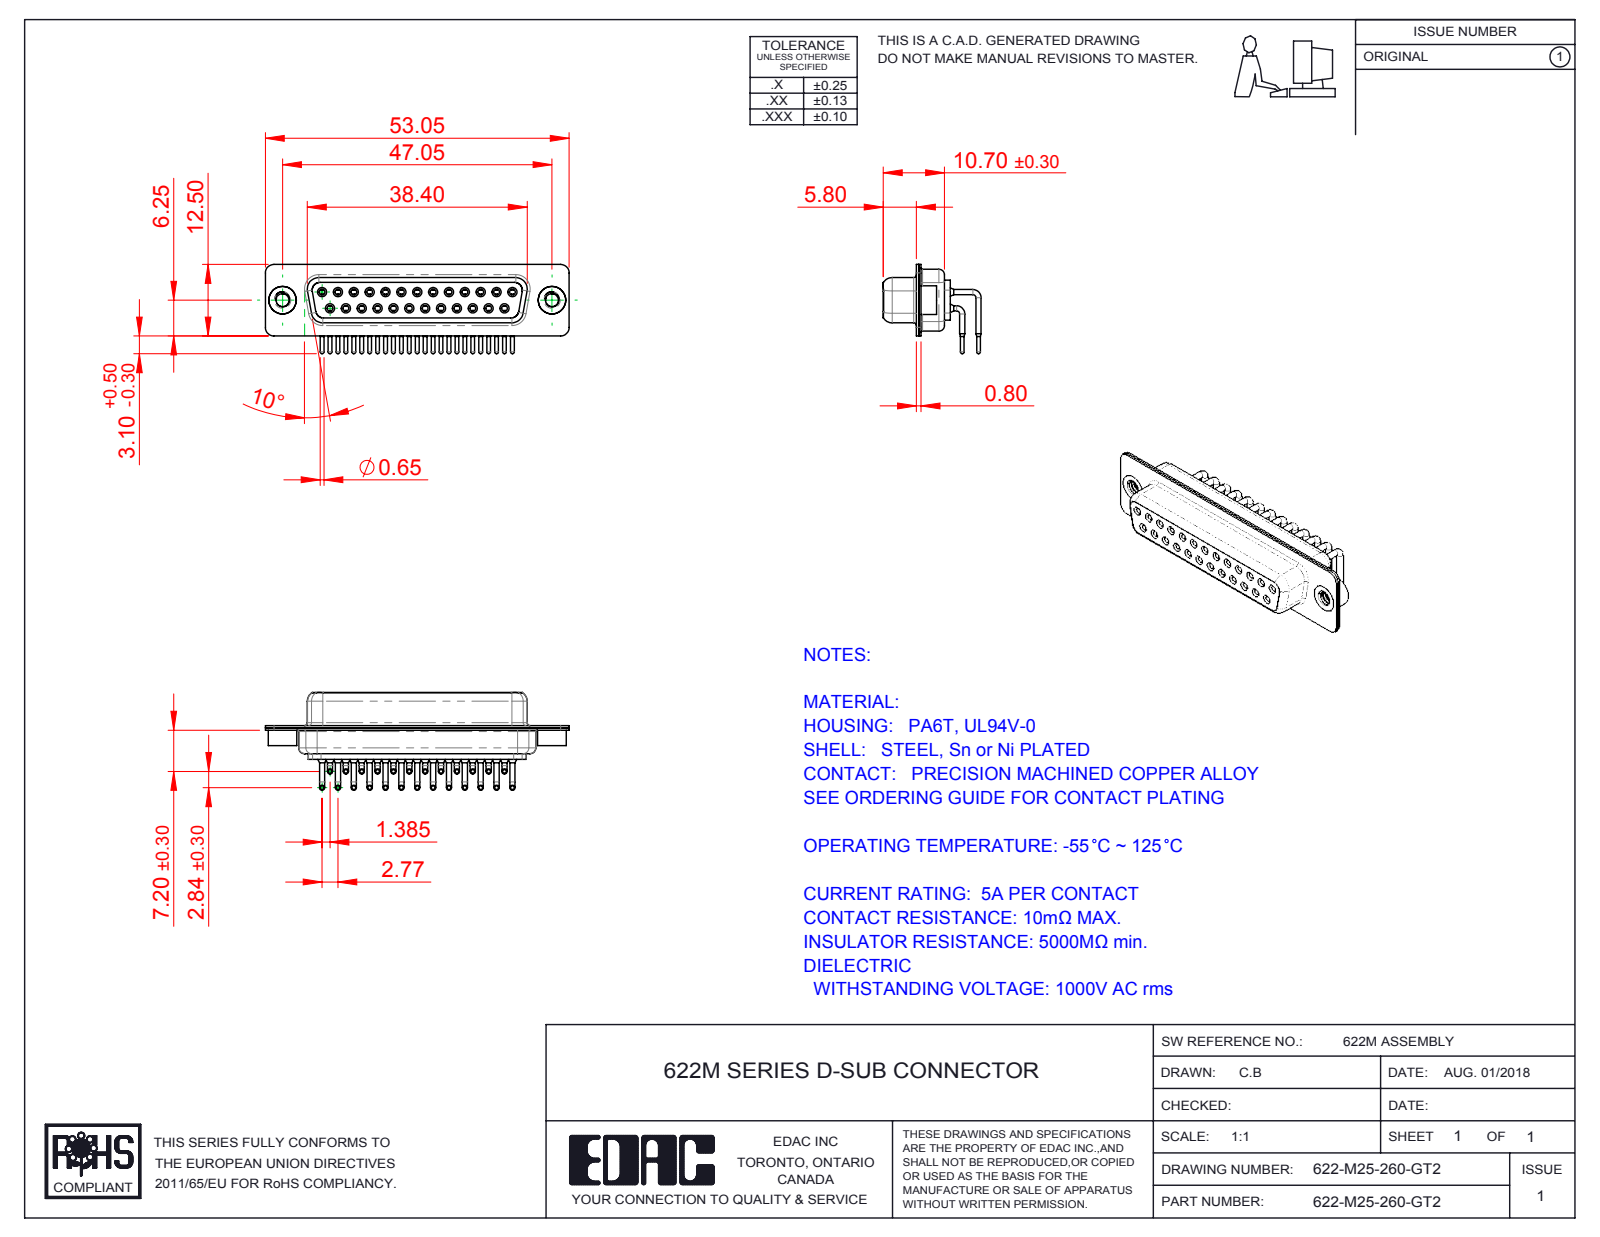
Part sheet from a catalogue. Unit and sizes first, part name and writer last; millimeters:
Units: millimetres
Overall size (bounding box): 53.05 × 17.09 × 15.6
Round holes (diameter × count): ⌀1 ×25, ⌀1.1 ×25, ⌀1.7 ×25, ⌀1.8 ×25, ⌀2 ×25, ⌀2.26 ×2, ⌀4 ×2, ⌀4.8 ×2
Round bosses / shafts (diameter × count): ⌀0.9 ×50, ⌀1.6 ×25, ⌀1.5 ×25, ⌀0.65 ×25, ⌀5 ×2, ⌀4.9 ×2
Partial cylindrical surfaces — rounded edges, fillets, slot ends (radius × count): R1.5 ×16, R2 ×12, R1.35 ×8, R1.6 ×8, R0.25 ×4, R0.5 ×4, R0.6 ×4, R0.65 ×4
Main face-to-face distances: 0.4, 1.45, 8.95, 6.2, 2.3, 1.9, 8.5, 0.45, 7.05, 0.85
Hole centre spacings: 3.16, 2.77, 5.54, 8.31, 11.08, 13.85, 16.62, 5.03
Volume: 3 852 mm³ · Surface area: 9 502 mm²
Bodies: 30 solids, 1604 faces (442 planar, 712 cylindrical, 450 other)
Part name (STEP PRODUCT): 622-M25-260-GT2; 622M 4-40 Threaded Rivet; 622M Contact Row 2; 622M Contact Row 1 (+3 more)
STEP written by: SolidWorks 2016 (CONFIG_CONTROL_DESIGN)
